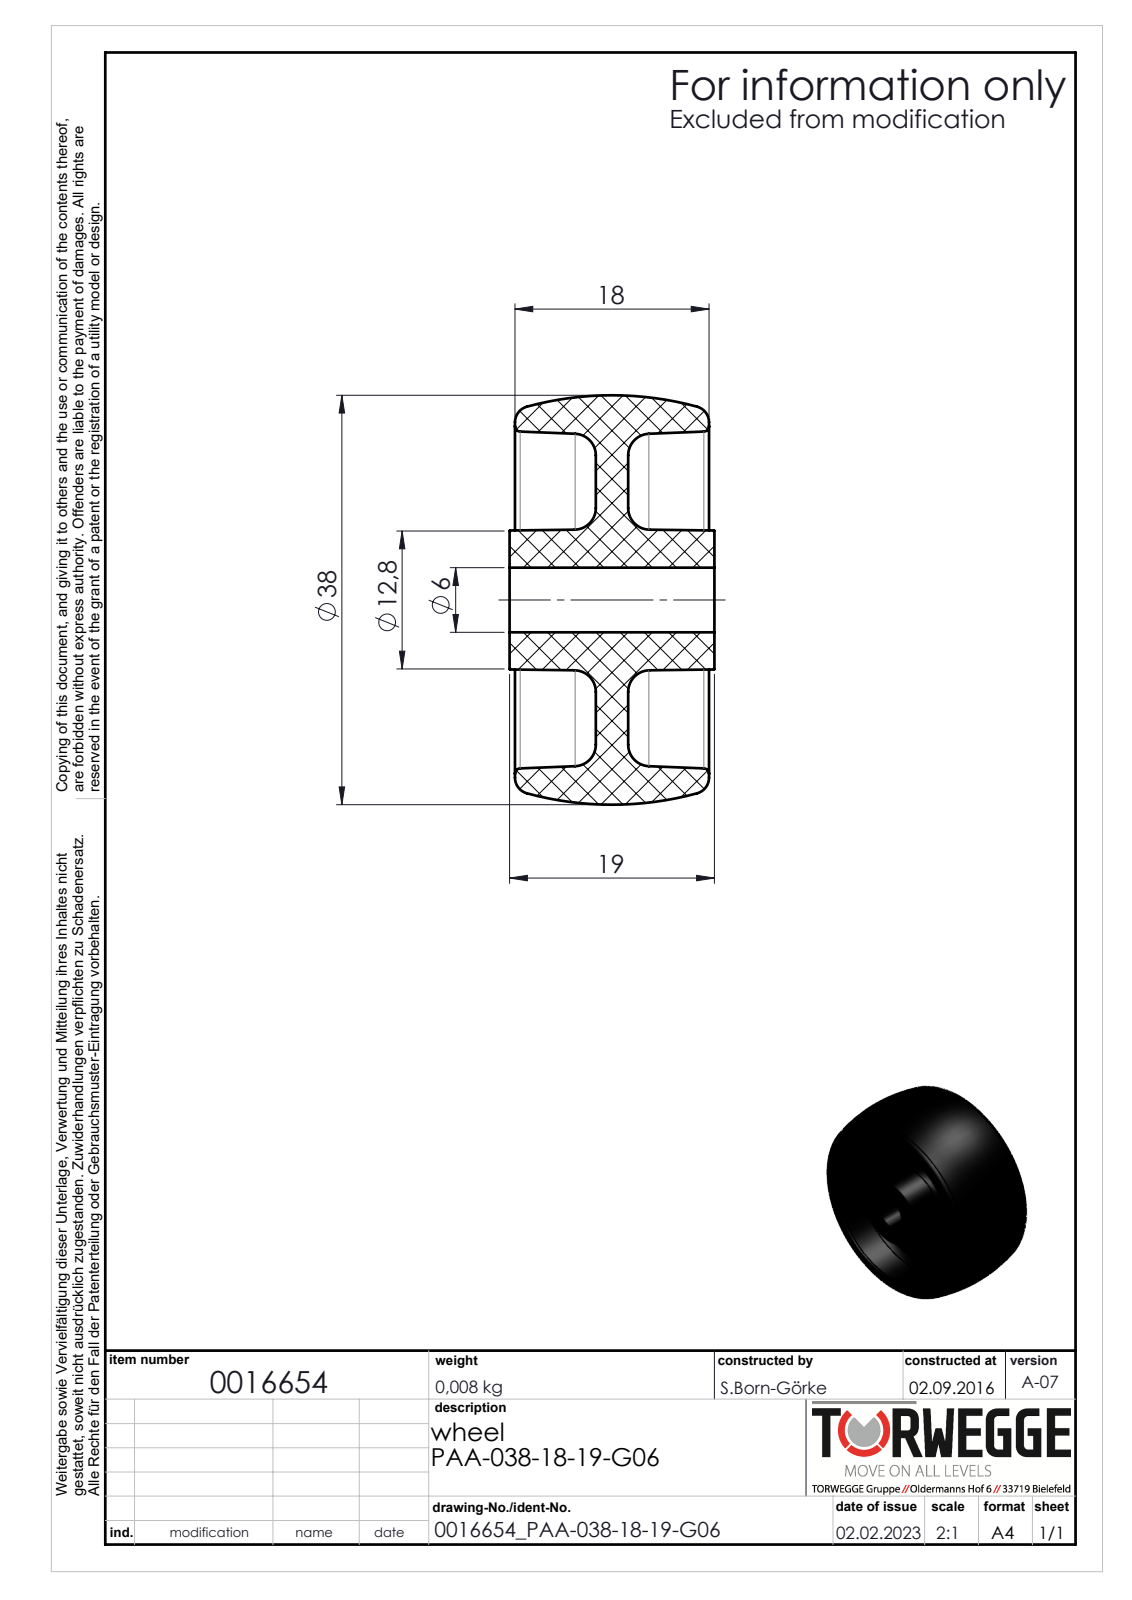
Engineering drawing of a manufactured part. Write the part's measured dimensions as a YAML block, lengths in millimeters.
part_name: "0016654"
step_written_by: "SolidWorks 2018 (AUTOMOTIVE_DESIGN)"
units: millimeters
bodies: {solids: 1, faces: 38, planar: 6, cylindrical: 2, other: 30}
overall_size: [38, 38, 19]
volume: 9877
surface_area: 6099
round_holes:
  - {diameter: 6, count: 1}
face_to_face_distances: [3, 8, 11, 19, 0.5, 18.5, 7.5, 10.5, 18]
